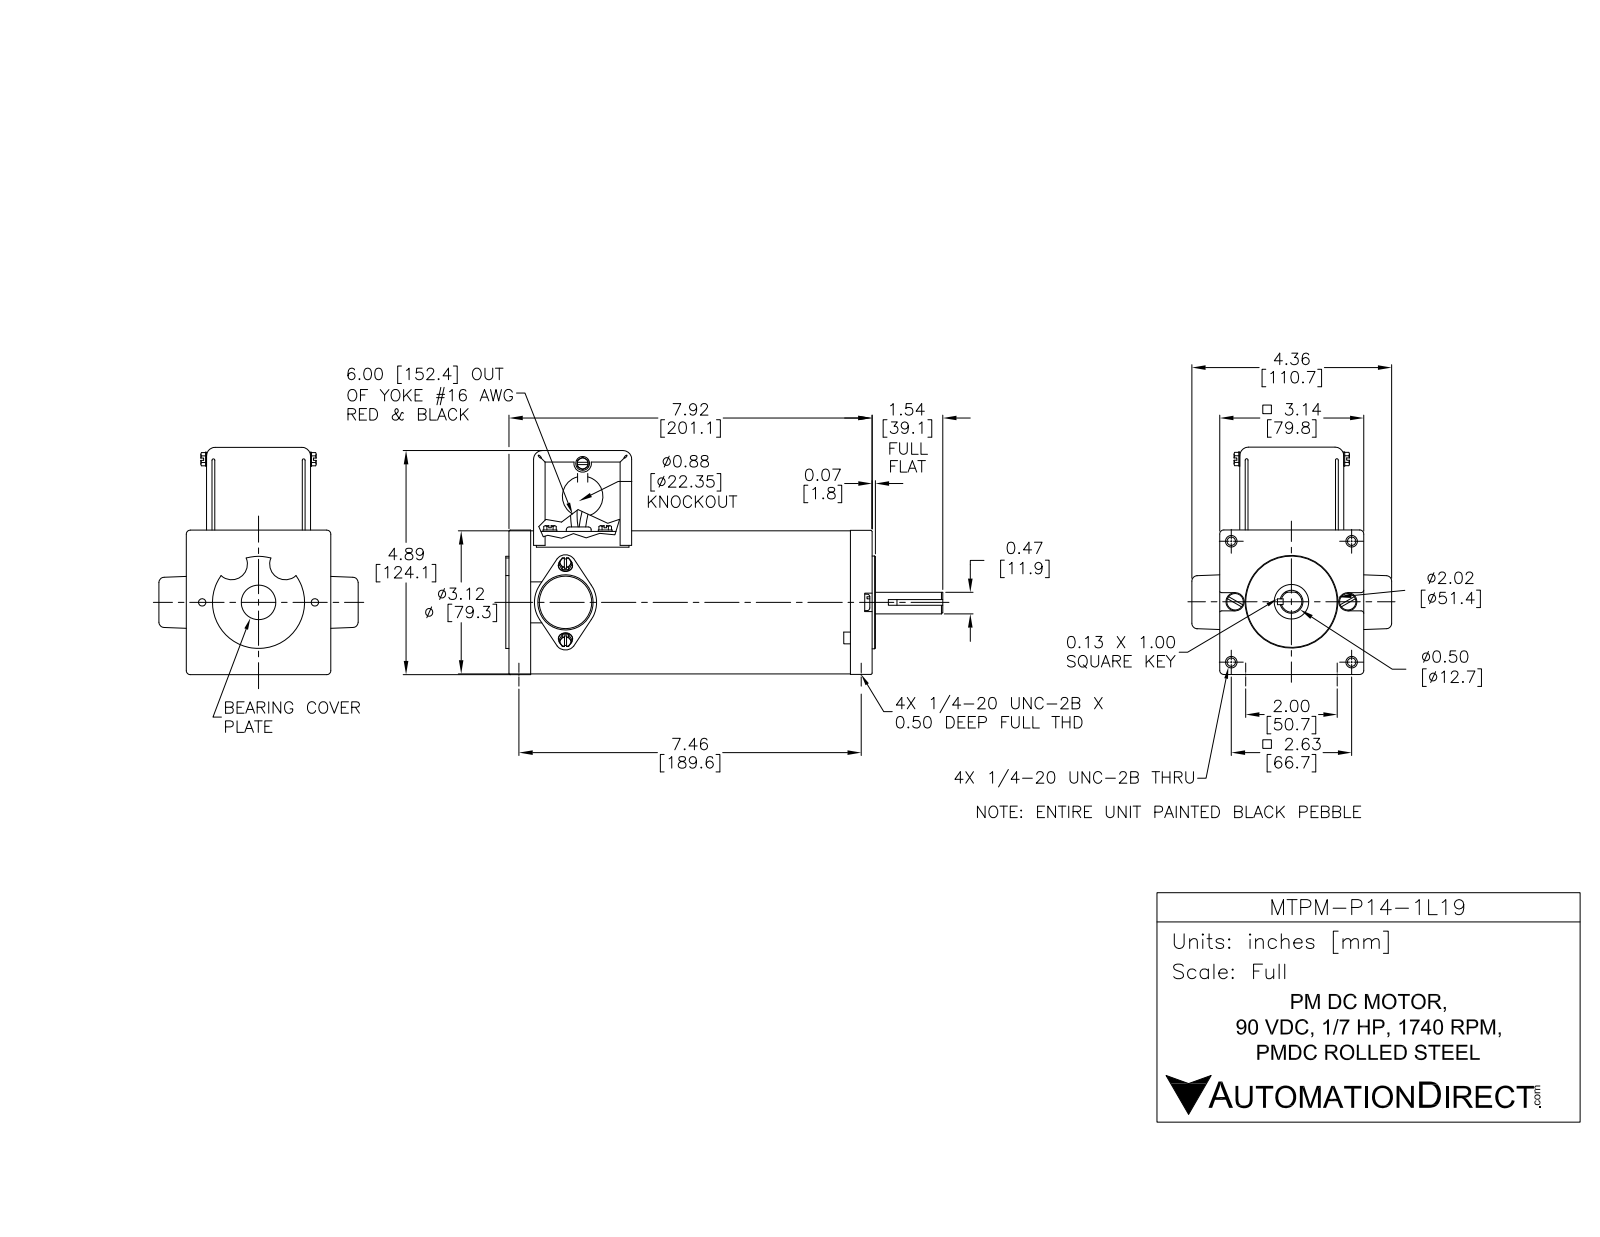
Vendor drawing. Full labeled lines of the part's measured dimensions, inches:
Part name (STEP PRODUCT): MTPM-P14-1L19
STEP written by: SolidWorks 2017 (AUTOMOTIVE_DESIGN)
Units: inches
Bodies: 28 solids, 409 faces (272 planar, 112 cylindrical, 25 other)
Overall size (bounding box): 9.52 × 4.944 × 4.39
Volume: 14.52 in³ · Surface area: 291.5 in²
Round holes (diameter × count): ⌀0.125 ×4, ⌀0.198 ×2, ⌀0.25 ×1, ⌀0.3 ×1, ⌀0.375 ×1, ⌀0.5 ×1, ⌀1.225 ×1, ⌀2.02 ×1, ⌀3 ×1, ⌀3.125 ×1
Round bosses / shafts (diameter × count): ⌀0.3 ×4, ⌀0.125 ×2, ⌀0.1 ×2, ⌀0.625 ×1, ⌀0.301 ×1
Partial cylindrical surfaces — rounded edges, fillets, slot ends (radius × count): R0.191 ×4, R0.234 ×4, R0.159 ×2, R0.341 ×2, R0.613 ×1, R0.667 ×1, R0.678 ×1, R1 ×1
Main face-to-face distances: 0.031, 0.25, 7.665, 0.063, 2.135, 7.415, 2.047, 0.094, 7.915, 2.198
Hole centre spacings: 1.318, 1.859, 2.63, 2.865, 1.23, 3.719, 2.46, 3.083
